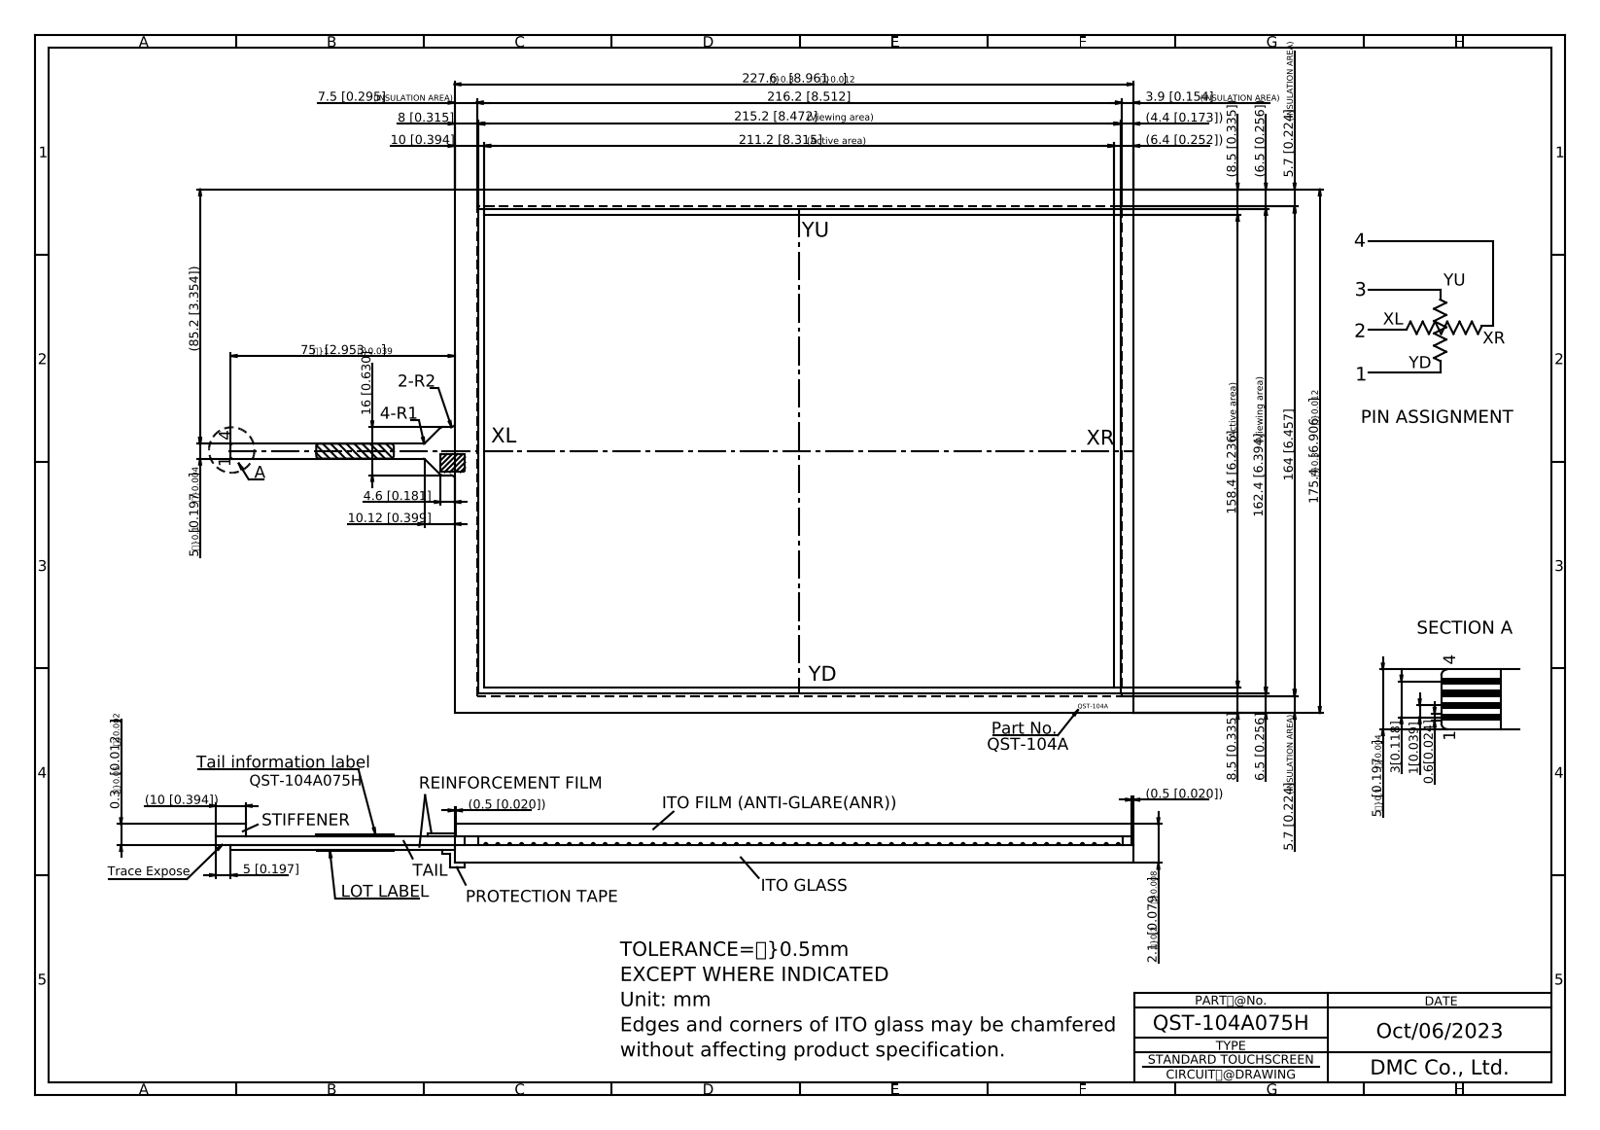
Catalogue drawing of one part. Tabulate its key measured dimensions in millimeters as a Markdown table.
| quantity | value |
| --- | --- |
| part name | QST-104A075H |
| STEP written by | Autodesk Inventor 2020 (CONFIG_CONTROL_DESIGN) |
| units | millimeters |
| bodies | 1 solid, 51 faces (45 planar, 6 cylindrical, 0 other) |
| overall size | 348.12 × 245.56 × 2.2 |
| volume | 83 743 mm³ |
| surface area | 82 618 mm² |
| partial cylindrical surfaces (radius × count) | 0.5 × 2, 1 × 2, 2 × 2 |
| main face-to-face distances | 2.1, 2, 175.4, 1.8, 1.9, 227.6, 0.4, 2.2, 6.5, 168.9 |
